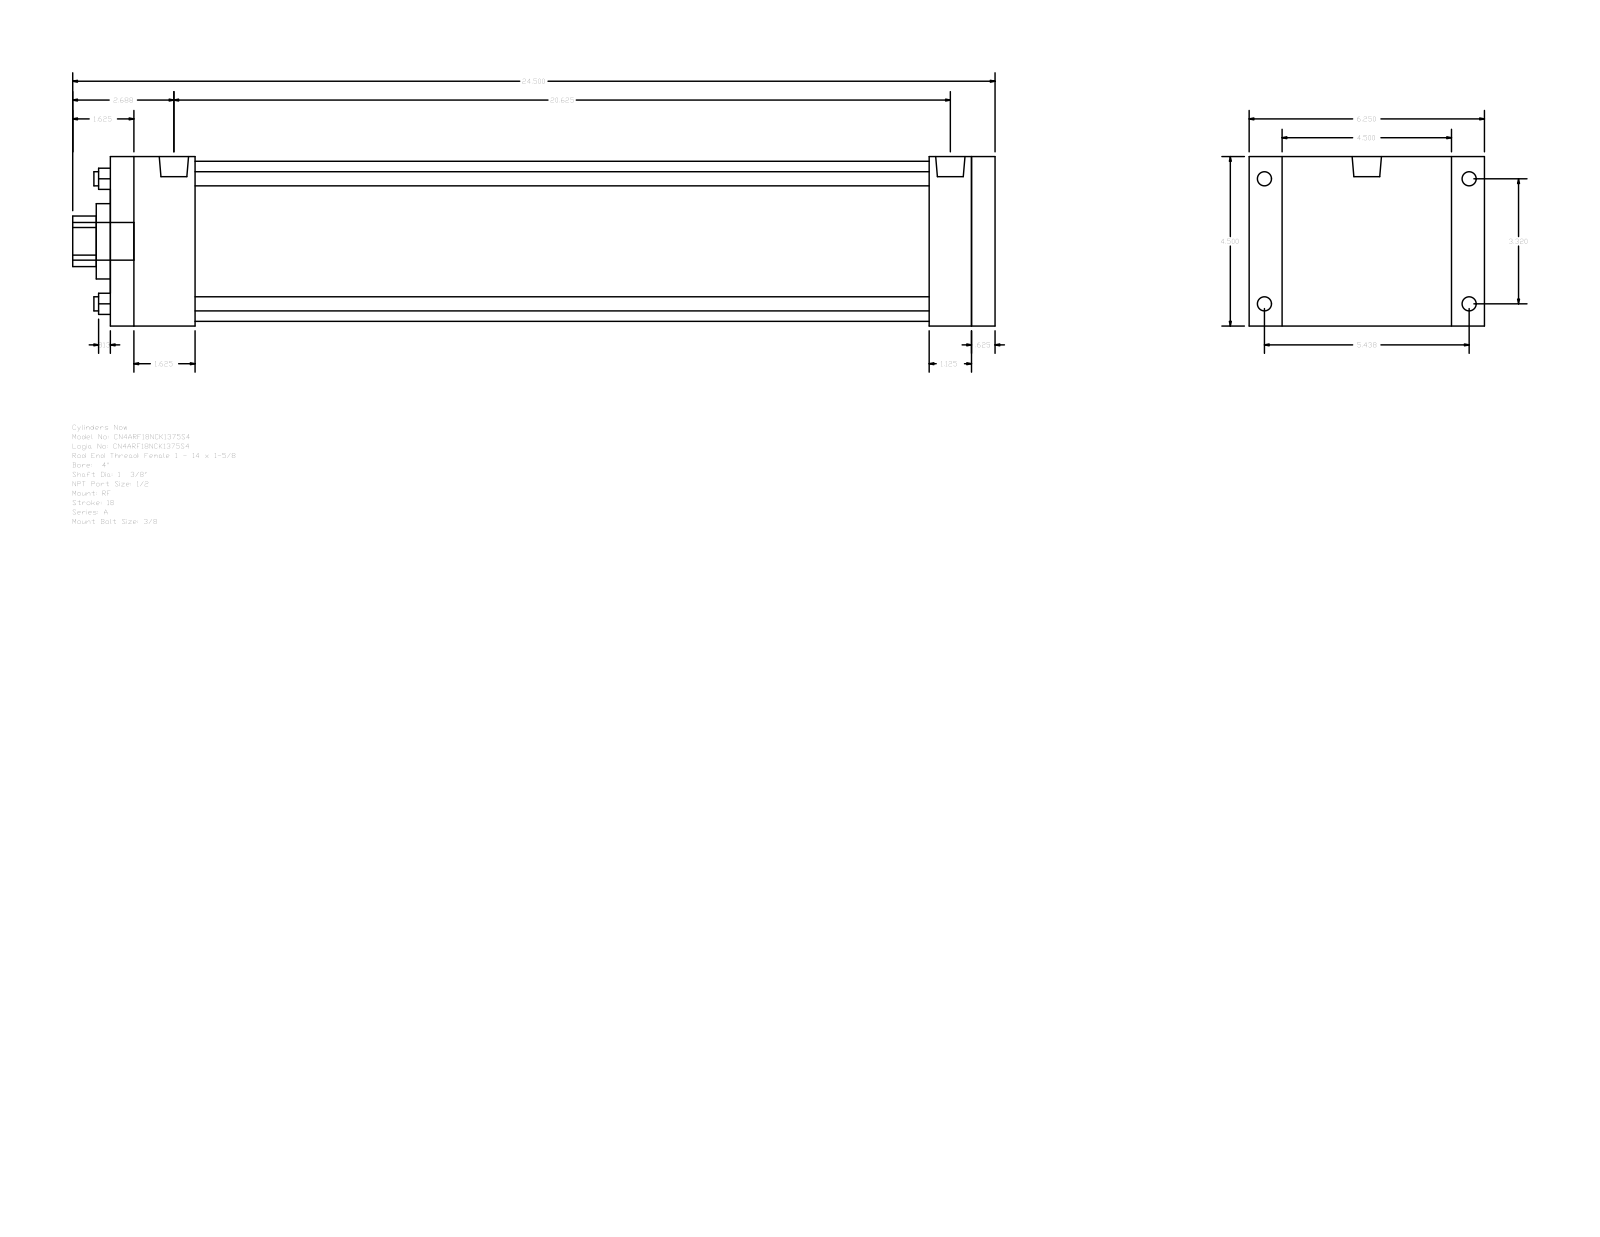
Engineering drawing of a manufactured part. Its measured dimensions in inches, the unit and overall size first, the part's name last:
Units: inches
Overall size (bounding box): 24.5 × 6.25 × 4.5
Round holes (diameter × count): ⌀0.375 ×4, ⌀1.375 ×1, ⌀2 ×1, ⌀4.25 ×1
Round bosses / shafts (diameter × count): ⌀0.375 ×4, ⌀0.344 ×4, ⌀0.778 ×2, ⌀1 ×1
Partial cylindrical surfaces — rounded edges, fillets, slot ends (radius × count): R0.672 ×1
Main face-to-face distances: 4.5, 23.5, 0.625, 22.875, 1.125, 0.875, 5.375, 21.75, 1.75, 2.25
Hole centre spacings: 2.347, 3.32, 4.695
Bodies: 0 solids, 92 faces (64 planar, 28 cylindrical, 0 other)
Part name (STEP PRODUCT): A_RF__0400_1.375
STEP written by: GSSL Pune (CONFIG_CONTROL_DESIGN)
